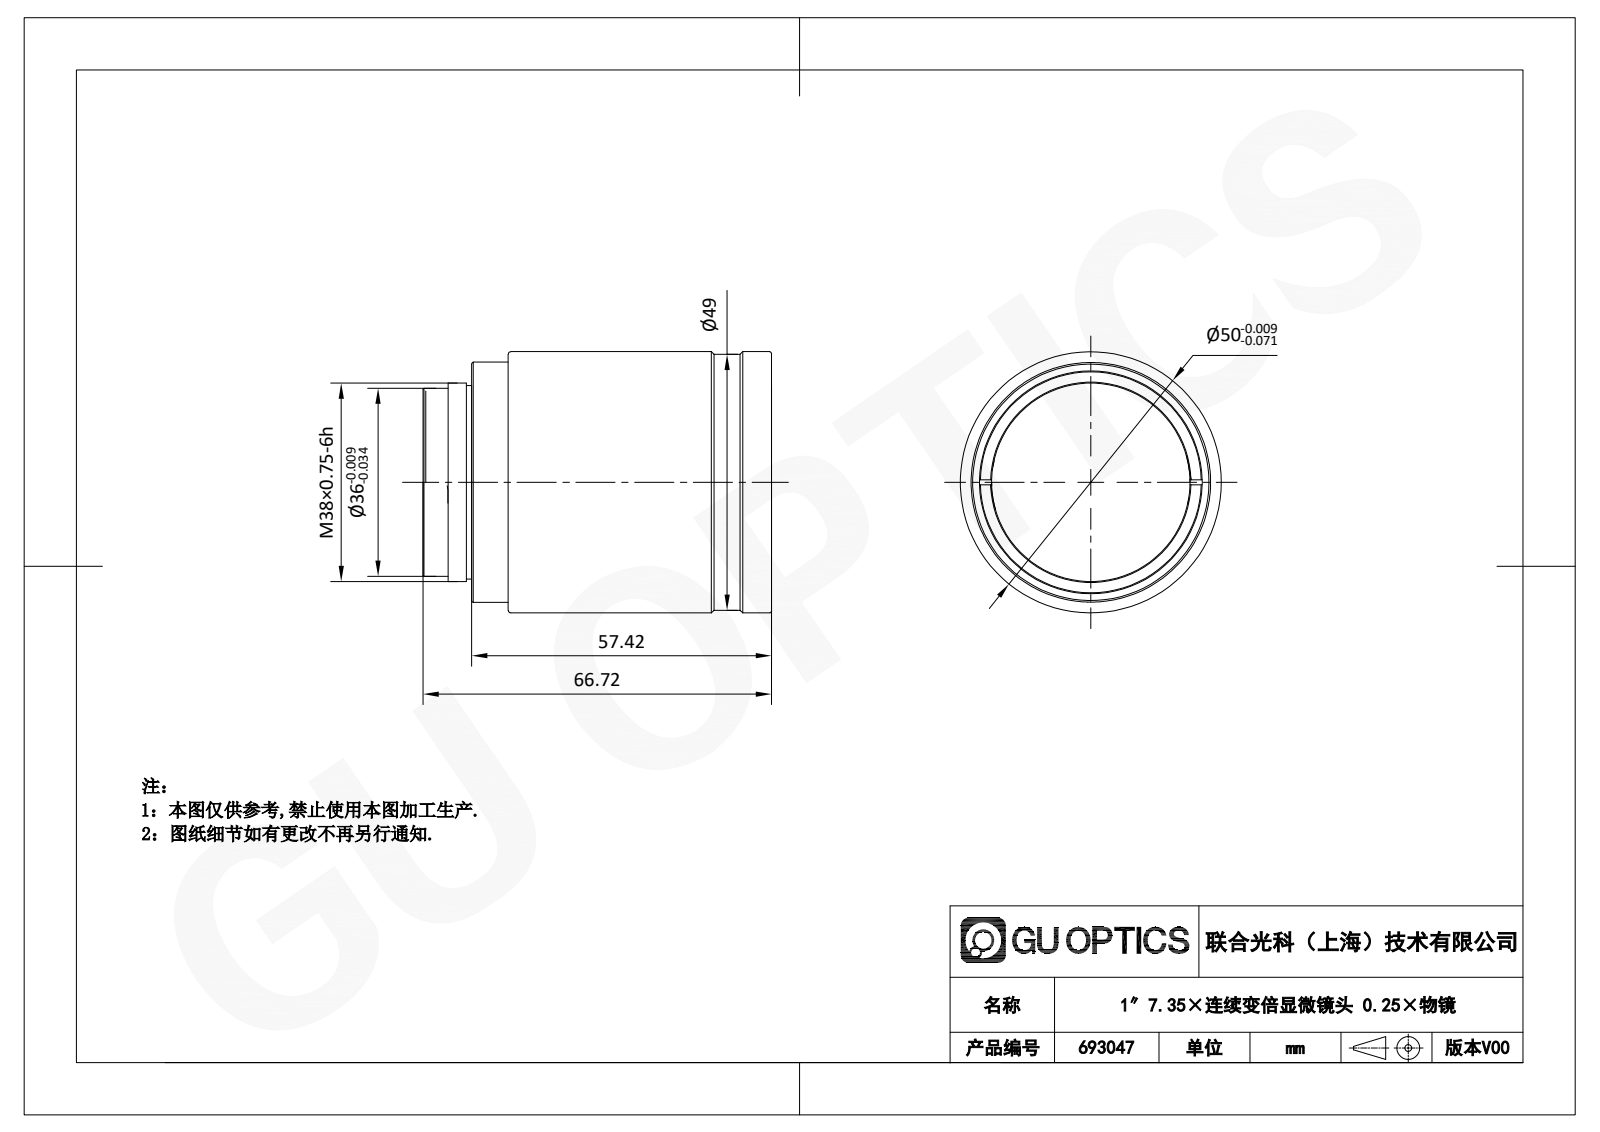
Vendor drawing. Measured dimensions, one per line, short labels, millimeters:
name: 693047
written by: SolidWorks 2020 (CONFIG_CONTROL_DESIGN)
unit: mm
bodies: 0 solids, 77 faces (16 planar, 12 cylindrical, 49 other)
size: 66.72 × 50 × 50
holes: 1× ⌀36, 1× ⌀37, 1× ⌀38, 1× ⌀45.25, 1× ⌀46.25
bosses: 1× ⌀50, 1× ⌀49, 1× ⌀45.98
rounds: 1× R17
face distances: 6.7, 7, 57.42, 4.5, 50.42, 57.12, 45.92, 52.62, 52.92, 4.67
